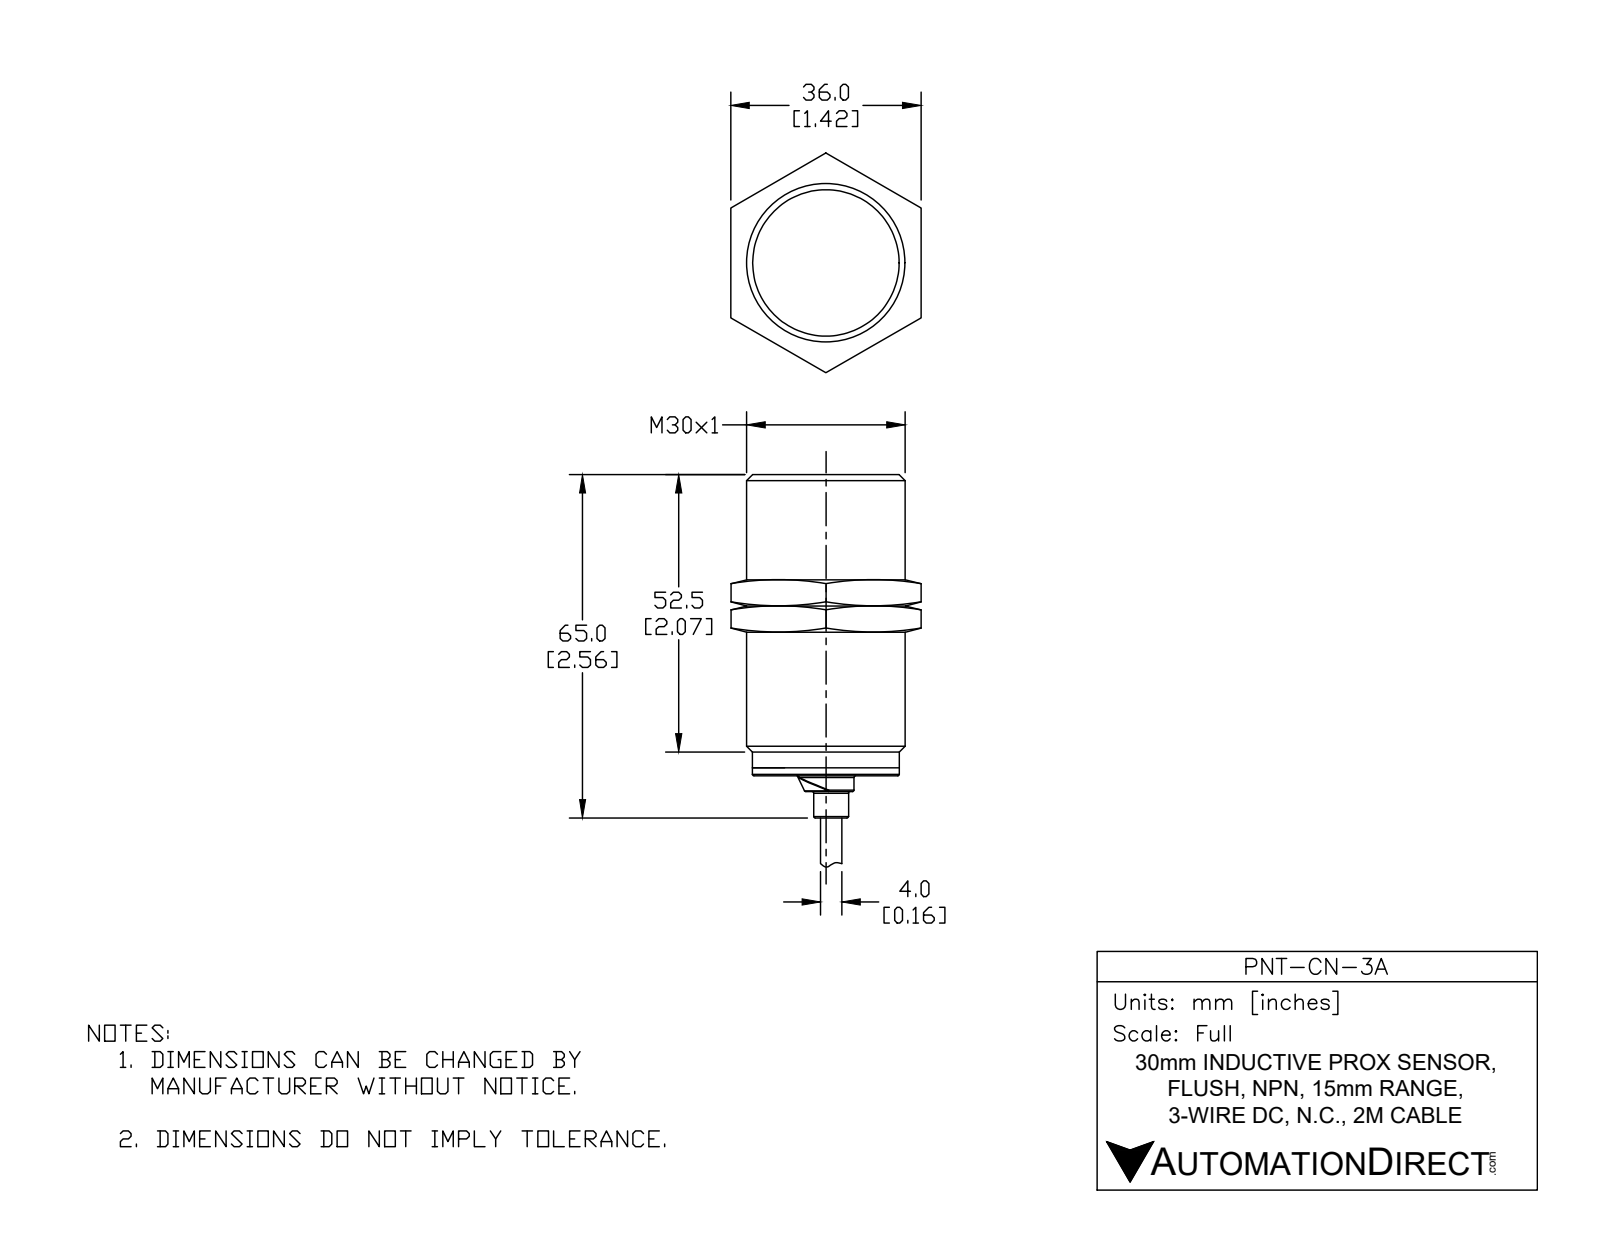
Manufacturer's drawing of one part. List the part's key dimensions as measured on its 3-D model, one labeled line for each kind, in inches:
Part name (STEP PRODUCT): PNT-CN-3A
STEP written by: SolidWorks 2017 (AUTOMOTIVE_DESIGN)
Units: inches
Bodies: 1 solid, 74 faces (14 planar, 30 cylindrical, 30 other)
Overall size (bounding box): 4.559 × 1.181 × 1.181
Volume: 2.487 in³ · Surface area: 11.9 in²
Round holes (diameter × count): ⌀0.162 ×1
Round bosses / shafts (diameter × count): ⌀0.049 ×6, ⌀1.181 ×1, ⌀1.095 ×1, ⌀1.094 ×1, ⌀0.417 ×1, ⌀0.26 ×1, ⌀0.157 ×1
Partial cylindrical surfaces — rounded edges, fillets, slot ends (radius × count): R0.077 ×1
Main face-to-face distances: 2.244, 2.362, 0.118, 2.28, 2.559, 0.315, 0.197, 4.559, 2.315, 2.197
